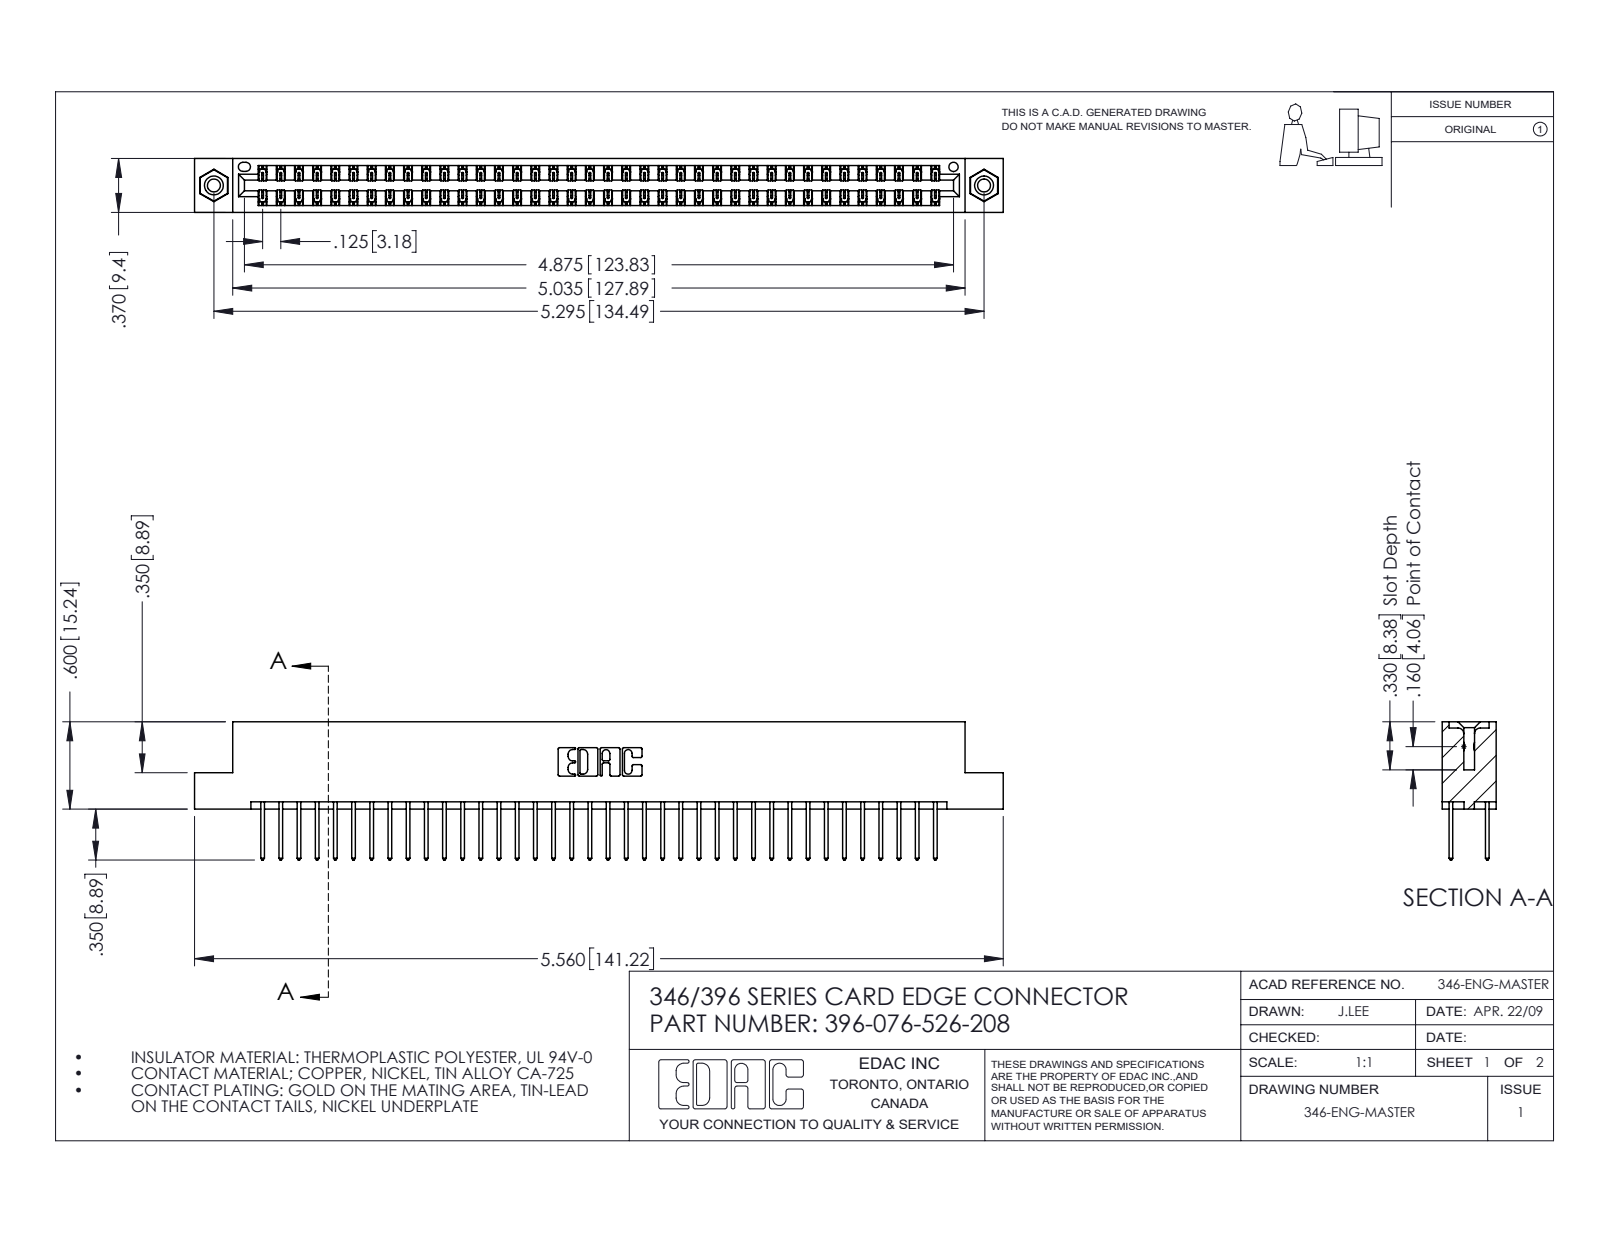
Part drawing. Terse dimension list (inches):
name: 345-292-001_345-293-126; 396-076-526-208; 345-250-001_345-250-003-102; 346 Part_Flush Mounting Lugs - 0.156 Dia-TI
written by: SolidWorks 2016 (CONFIG_CONTROL_DESIGN)
unit: in
bodies: 79 solids, 4134 faces (2768 planar, 1350 cylindrical, 16 other)
size: 5.56 × 0.95 × 0.37
volume: 0.846 in³; area: 30.32 in²
holes: 2× ⌀0.089, 2× ⌀0.125, 2× ⌀0.156, 1× ⌀0.064
bosses: 2× ⌀0.155
rounds: 114× R0.006, 76× R0.01, 22× R0.01, 6× R0.007, 6× R0.031, 3× R0.026, 2× R0.014, 2× R0.022
face distances: 0.048, 0.322, 0.25, 0.37, 0.072, 0.298, 0.025, 0.275, 0.148, 0.222
hole spacings: 0.246, 5.086, 5.295
